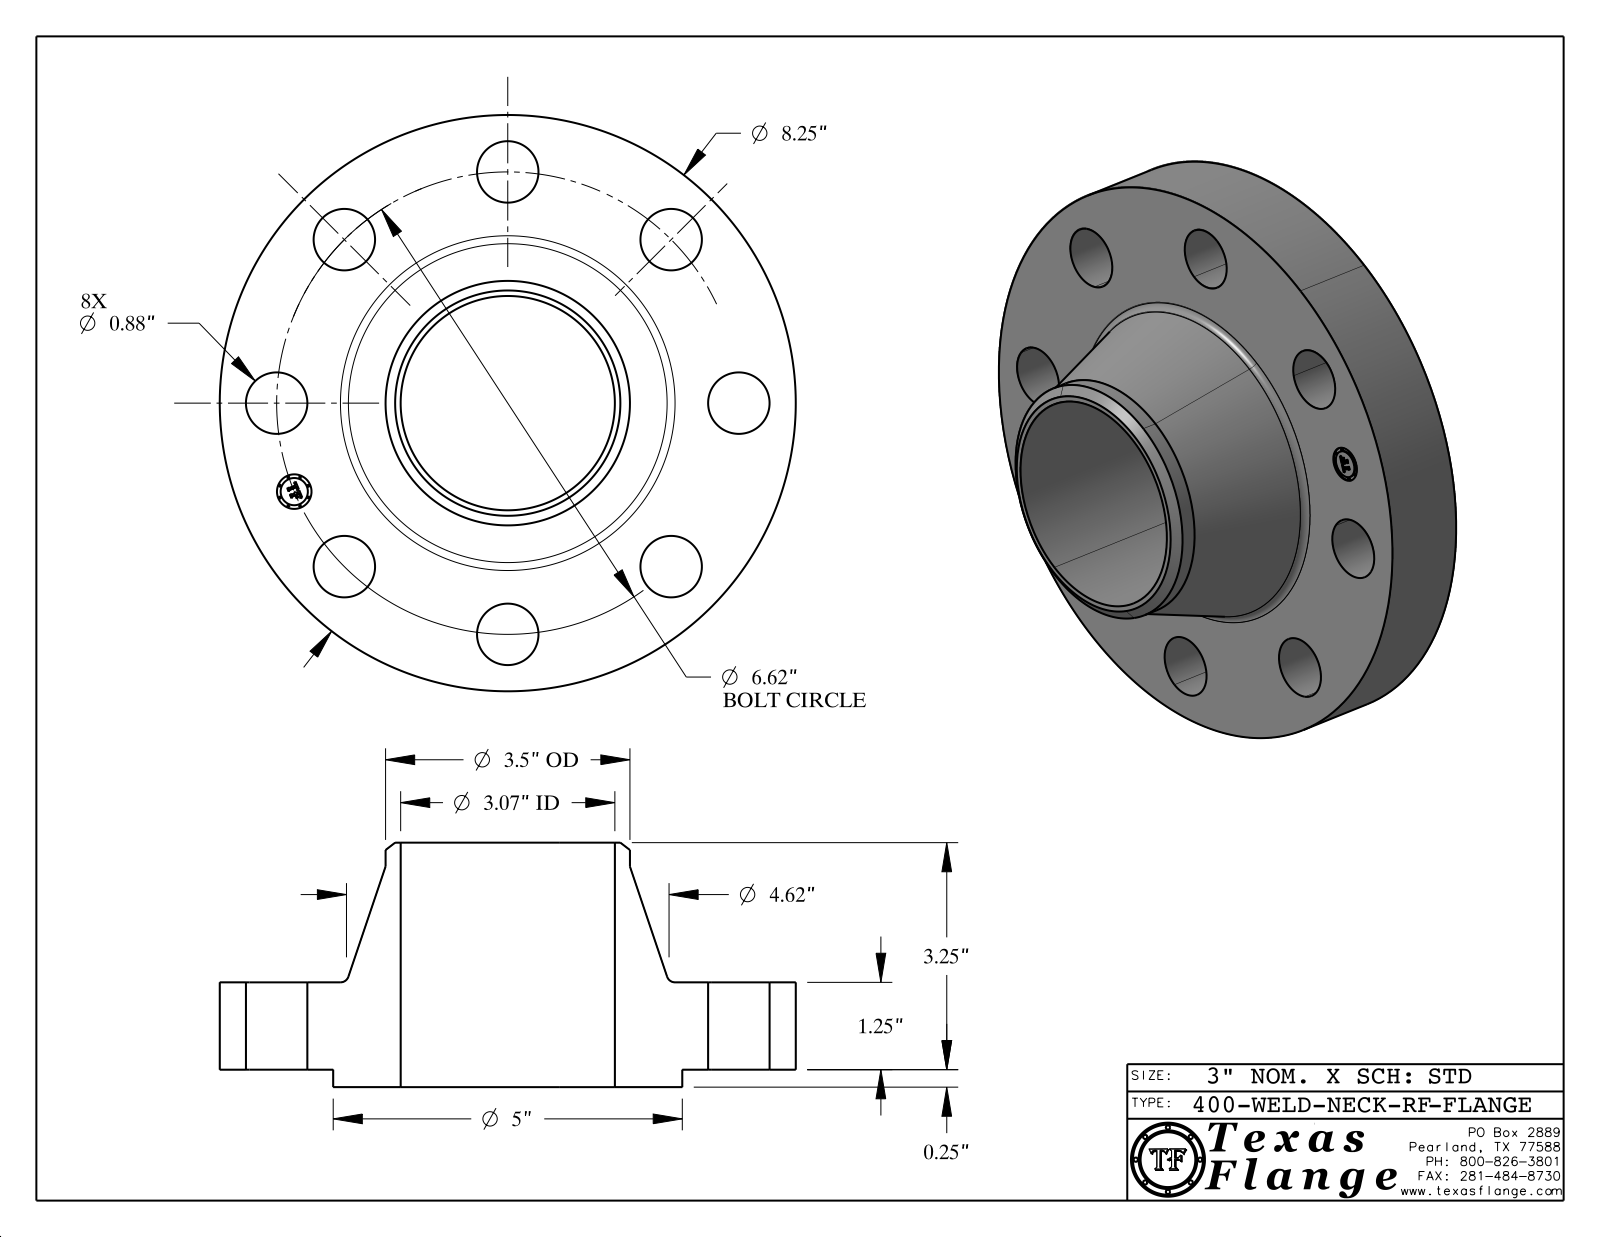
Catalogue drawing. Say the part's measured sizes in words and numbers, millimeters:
The part is named "400-WELD-NECK-RF". Its 3-D file was written by "CATIA V5 STEP AP214 (AUTOMOTIVE_DESIGN)". It is 1 solid with 419 faces: 369 planar, 44 cylindrical and 6 other. Overall it measures 209.6 by 209.6 by 88.9 millimeters. Its volume is 1 059 000 cubic millimeters and its surface area 127 700 square millimeters. Round holes: 8 of diameter 22.4, 1 of diameter 12.6, 1 of diameter 77.9. Round bosses or shafts: 8 of diameter 0.8, 1 of diameter 209.6, 1 of diameter 127, 1 of diameter 88.9, 1 of diameter 9.9. The main face-to-face distances are 31.8, 6.4, 38.1, 88.9, 82.6, 50.8, 0.4, 37.7, 31.4, 51.2. The hole center spacings are 84.1, 64.3, 155.3, 118.9, 118.9, 32.8, 93.4, 164.9.
